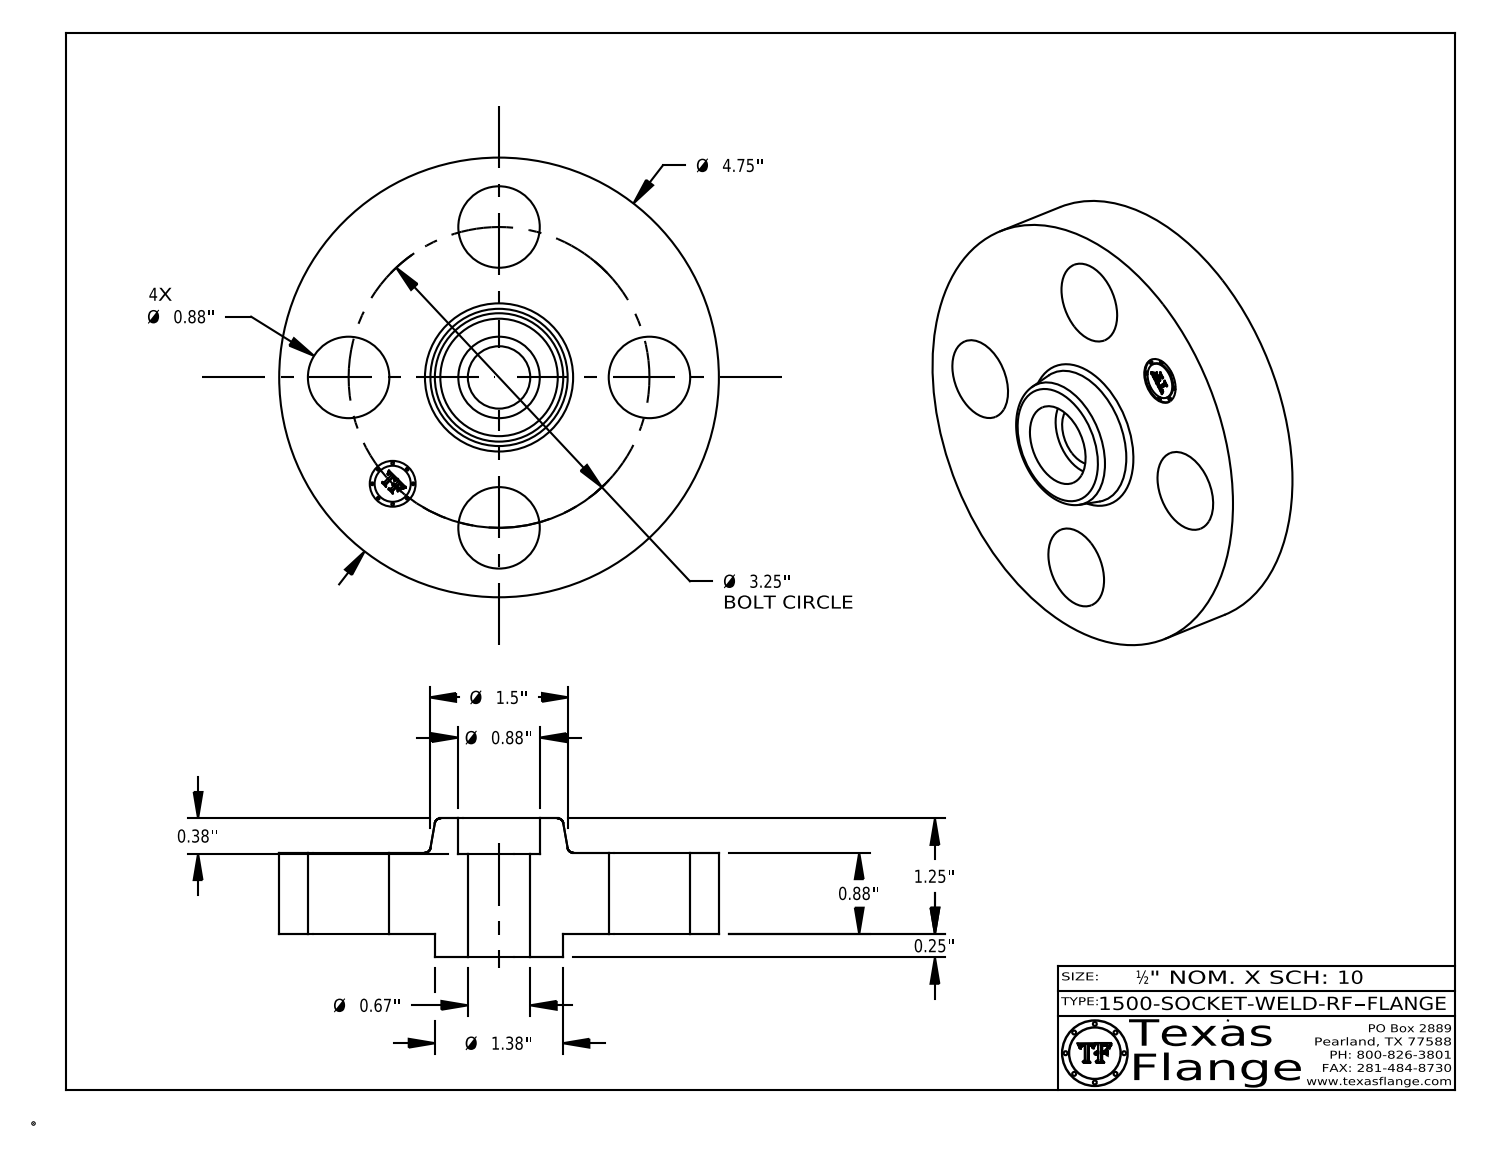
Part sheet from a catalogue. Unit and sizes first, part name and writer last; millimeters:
Units: millimetres
Overall size (bounding box): 120.7 × 120.7 × 38.1
Round holes (diameter × count): ⌀22.4 ×5, ⌀12.6 ×1, ⌀17.1 ×1
Round bosses / shafts (diameter × count): ⌀0.8 ×8, ⌀120.7 ×1, ⌀35.1 ×1, ⌀9.9 ×1
Main face-to-face distances: 22.4, 6.4, 28.7, 38.1, 31.8, 9.4, 28.4, 22.1, 9.7, 28.3
Hole centre spacings: 41.3, 58.4, 31.6, 76.3, 82.6
Volume: 226 000 mm³ · Surface area: 37 790 mm²
Bodies: 1 solid, 412 faces (370 planar, 36 cylindrical, 6 other)
Part name (STEP PRODUCT): 1500-SOCKET-WELD-RF
STEP written by: CATIA V5 STEP AP214 (AUTOMOTIVE_DESIGN)
